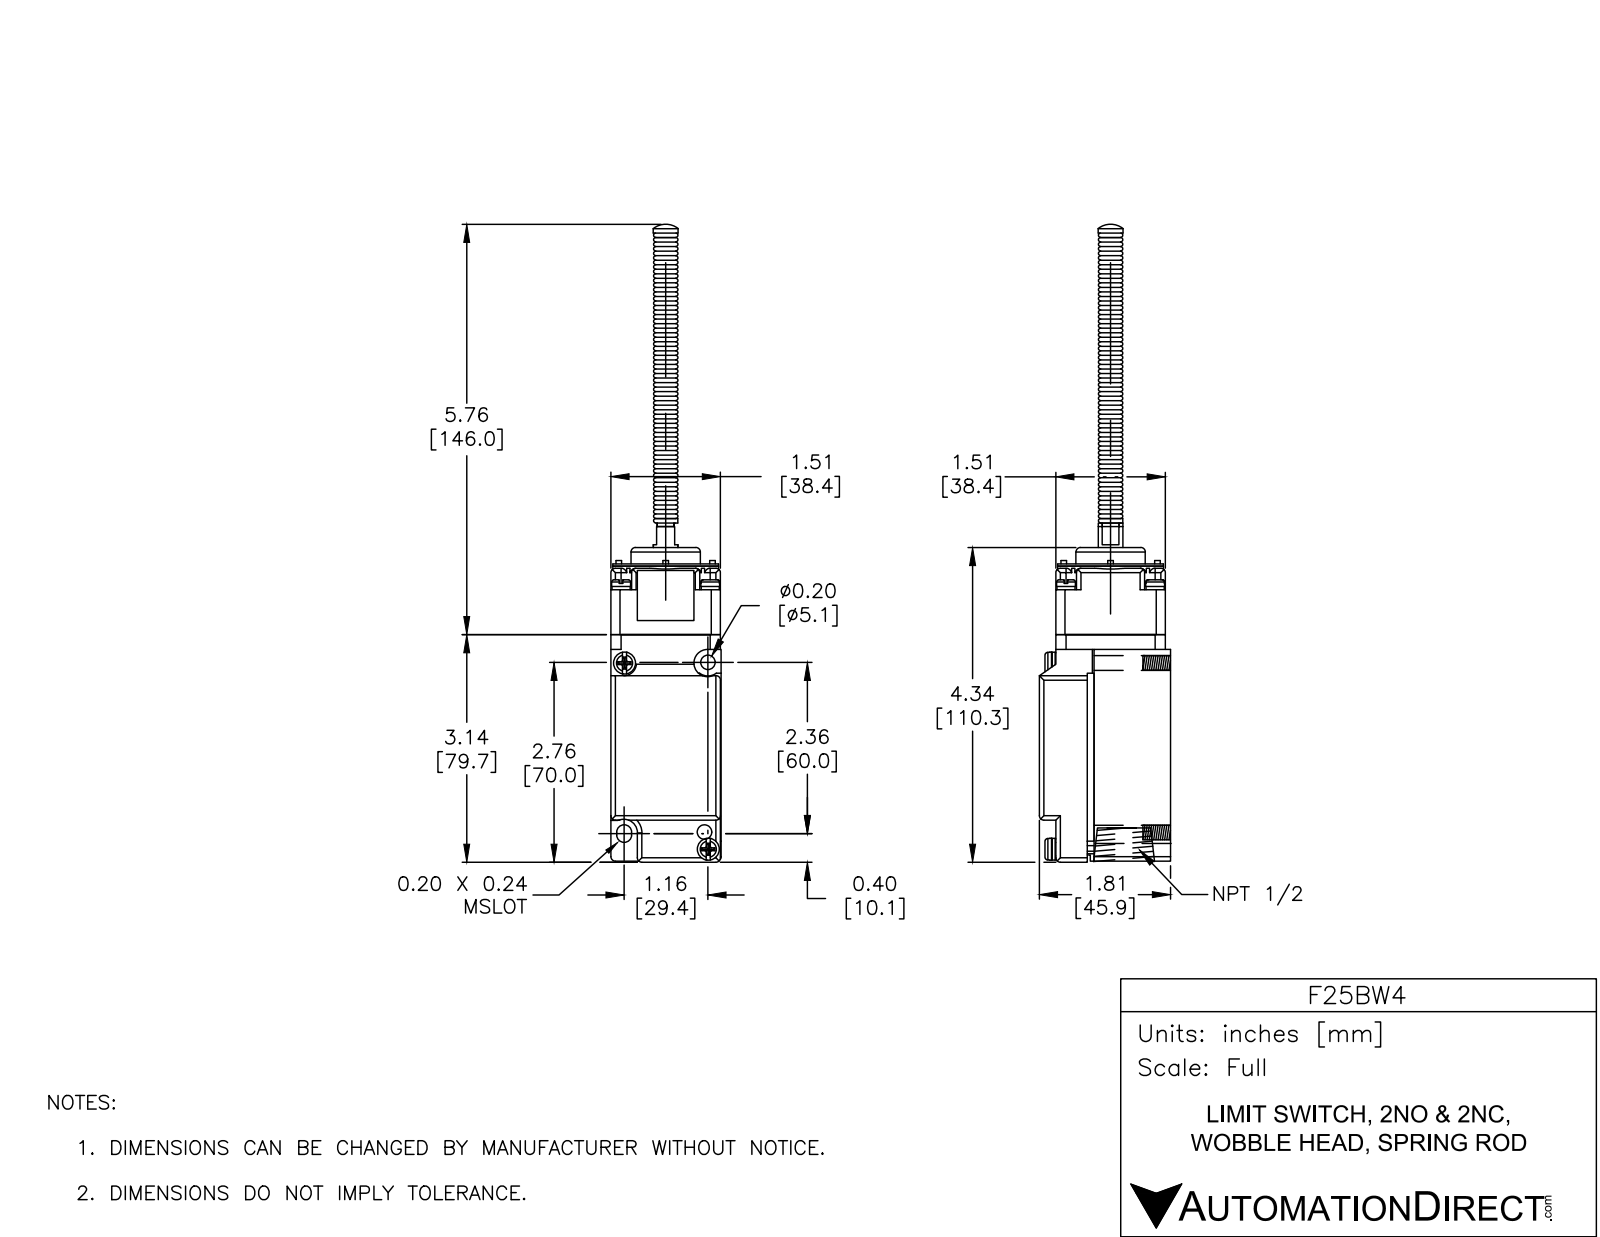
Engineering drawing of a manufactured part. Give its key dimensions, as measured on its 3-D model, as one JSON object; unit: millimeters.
{"part_name": "F25BW4", "step_written_by": "SolidWorks 2018 (AUTOMOTIVE_DESIGN)", "units": "millimeters", "bodies": {"solids": 80, "faces": 795, "planar": 255, "cylindrical": 142, "other": 398}, "overall_size": [223.5, 45.9, 38.6], "volume_mm3": 166500, "surface_area_mm2": 55050, "round_holes": [[2, 4], [4.5, 4], [4.8, 3], [5.1, 3], [5.8, 1], [23.4, 1], [26.8, 1]], "round_bosses_or_shafts": [[6.4, 5], [6.6, 4], [3.6, 4], [7.7, 2], [7.6, 2], [37, 1], [24.3, 1], [10.2, 1]], "partial_cylinders_radius": [[1.6, 21], [0.8, 16], [0.4, 8], [1.6, 8], [3.6, 4], [3.7, 4], [2.6, 2], [4.8, 2]], "face_to_face_distances": [2.4, 29.2, 26.8, 38.6, 24, 16.8, 19.2, 45.9, 38.4, 11], "hole_center_spacings": [35.6, 15.6, 16.4, 15.6, 22.1, 22.1, 23.2, 23.2]}
